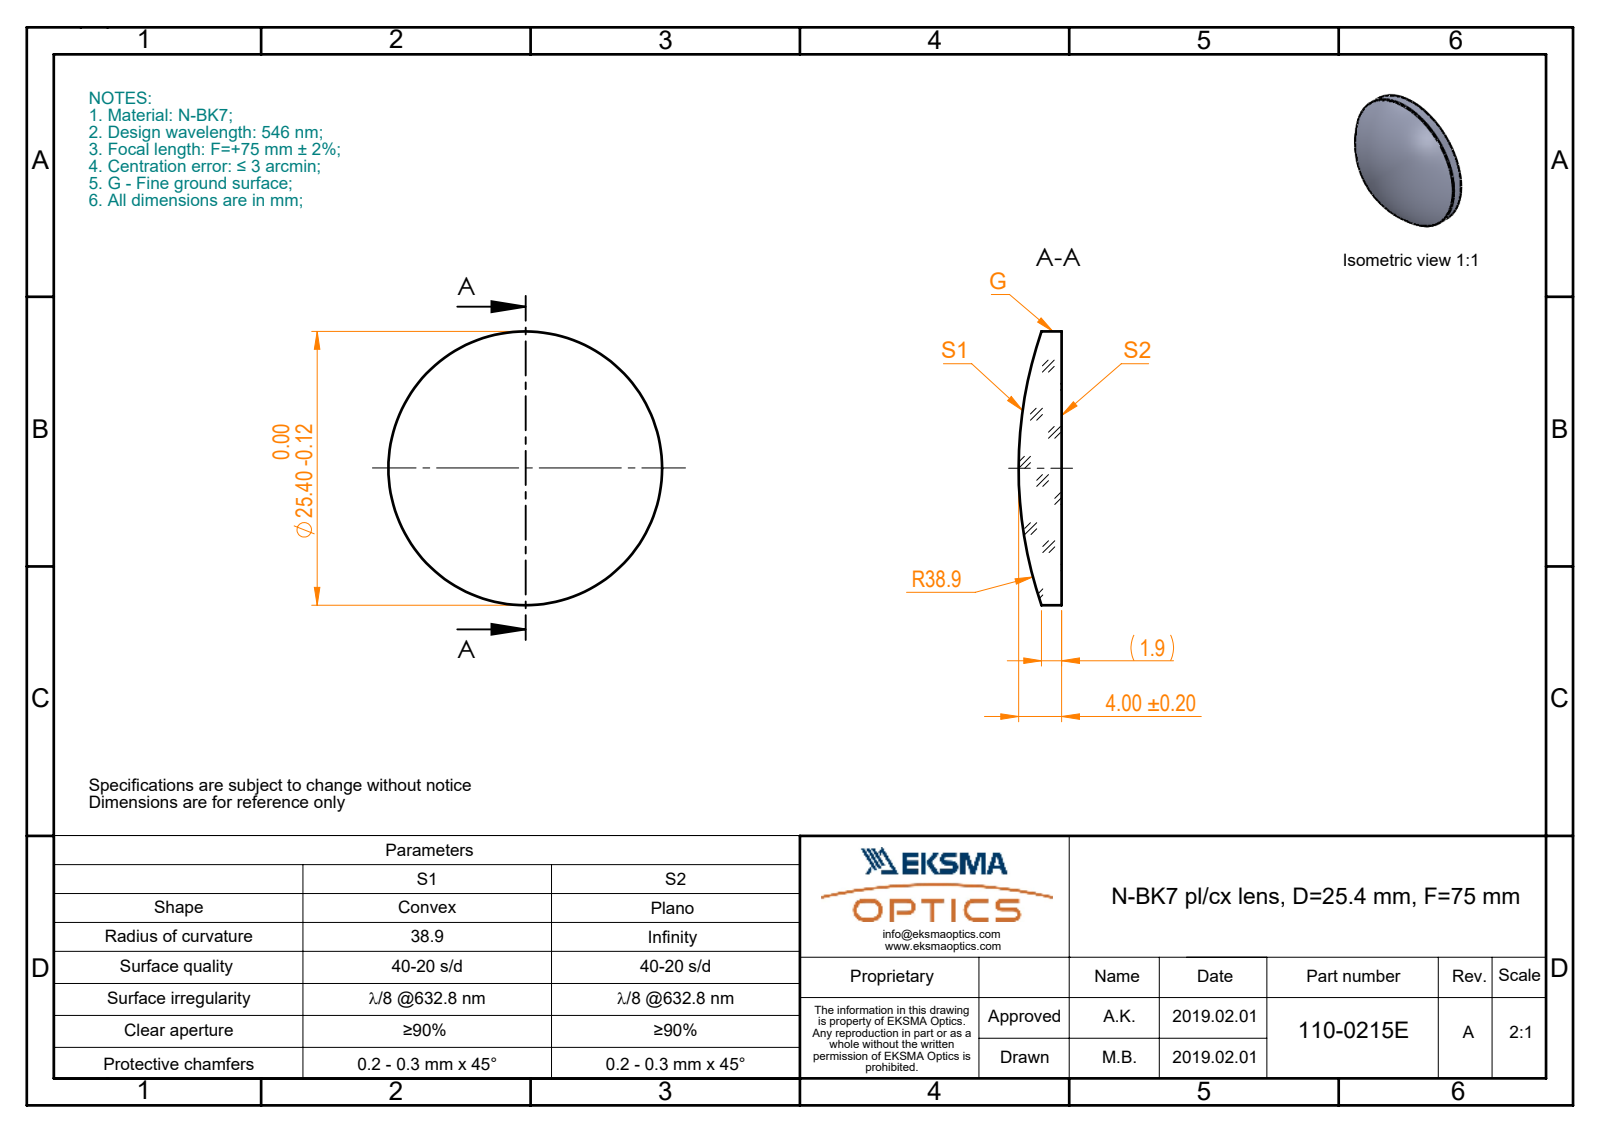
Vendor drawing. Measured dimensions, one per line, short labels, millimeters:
name: 110-0215E BK7 pl-cx 25.4 F75
written by: SolidWorks 2017 (CONFIG_CONTROL_DESIGN)
unit: mm
bodies: 1 solid, 5 faces (1 planar, 2 cylindrical, 2 other)
size: 25.4 × 25.4 × 4
volume: 1 492 mm³; area: 1 177 mm²
bosses: 1× ⌀25.4
